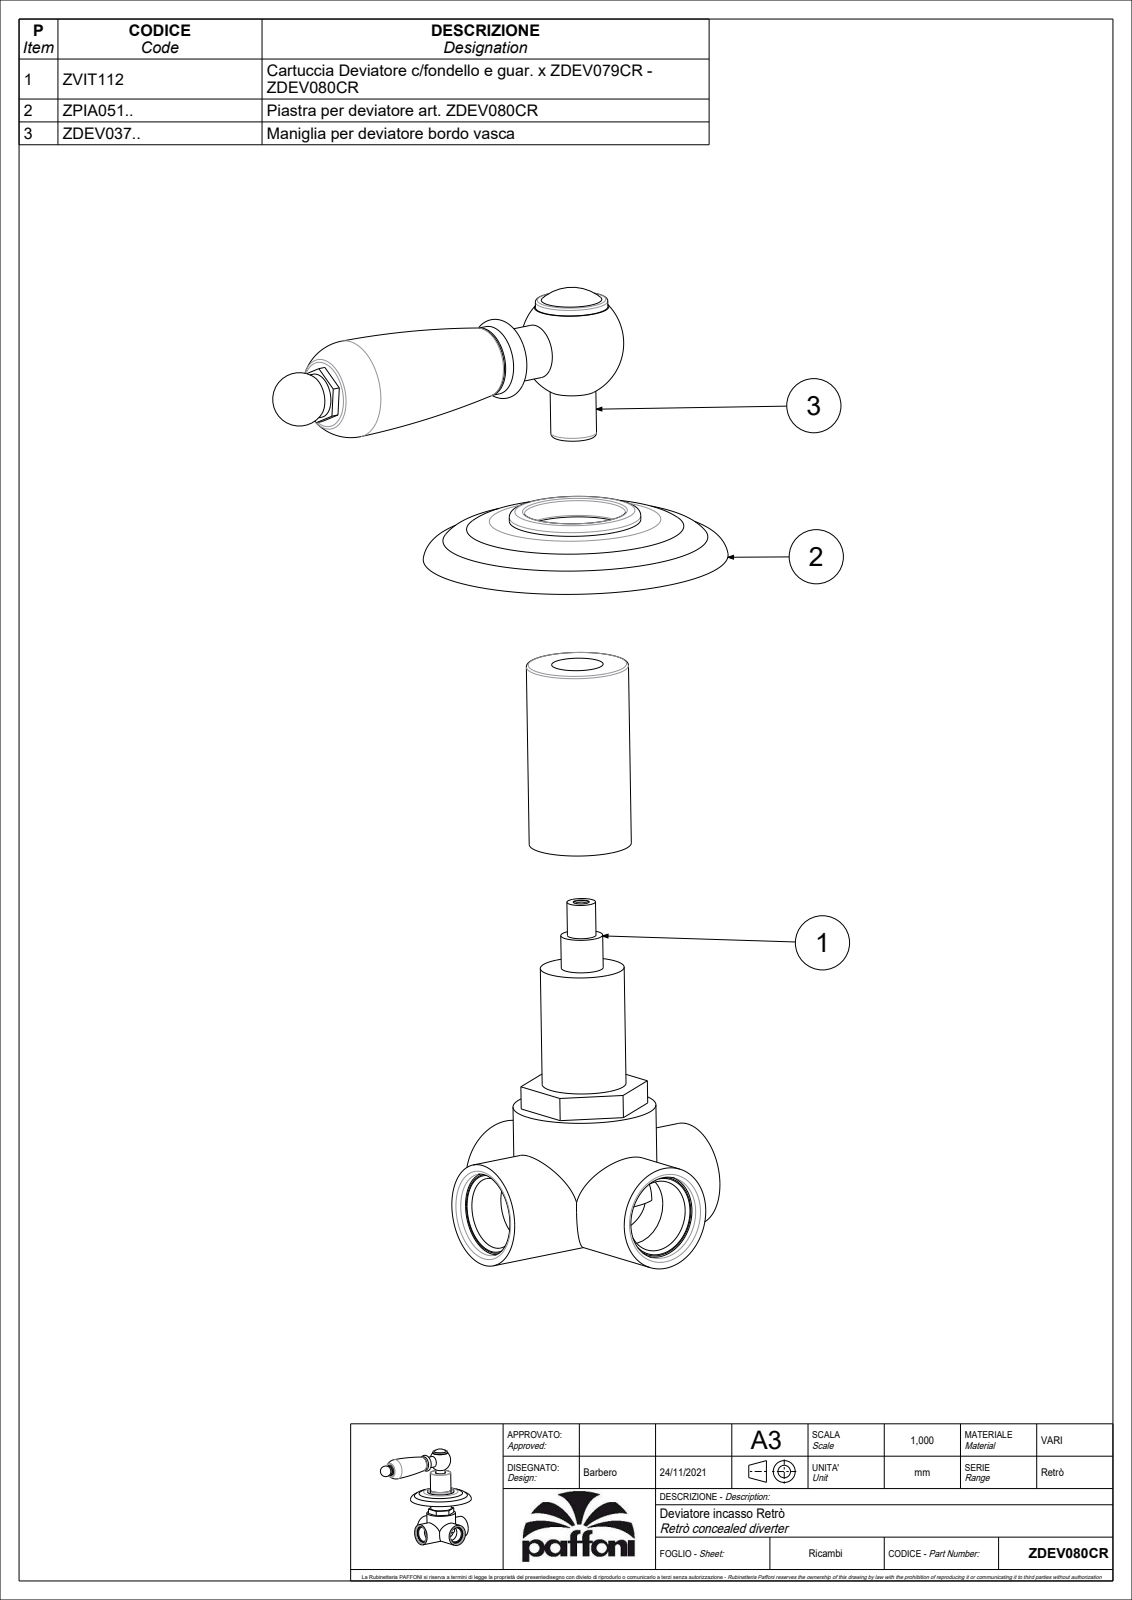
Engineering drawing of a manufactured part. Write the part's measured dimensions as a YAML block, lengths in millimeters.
part_name: "ZDEV080CR"
step_written_by: "CREO PARAMETRIC BY PTC INC, 2020044 (CONFIG_CONTROL_DESIGN)"
units: millimeters
bodies: {solids: 1, faces: 96, planar: 26, cylindrical: 30, other: 40}
overall_size: [137.4, 80, 67.7]
volume: 72073
surface_area: 26190
round_holes:
  - {diameter: 13.5, count: 1}
  - {diameter: 20.7, count: 1}
  - {diameter: 24, count: 1}
  - {diameter: 60, count: 1}
round_bosses_or_shafts:
  - {diameter: 34.5, count: 1}
  - {diameter: 31, count: 1}
  - {diameter: 27, count: 1}
  - {diameter: 22, count: 1}
  - {diameter: 19, count: 1}
  - {diameter: 18, count: 1}
  - {diameter: 14, count: 1}
  - {diameter: 12, count: 1}
face_to_face_distances: [1, 10, 9, 36, 27, 26, 2, 3.5, 23.5, 8]
